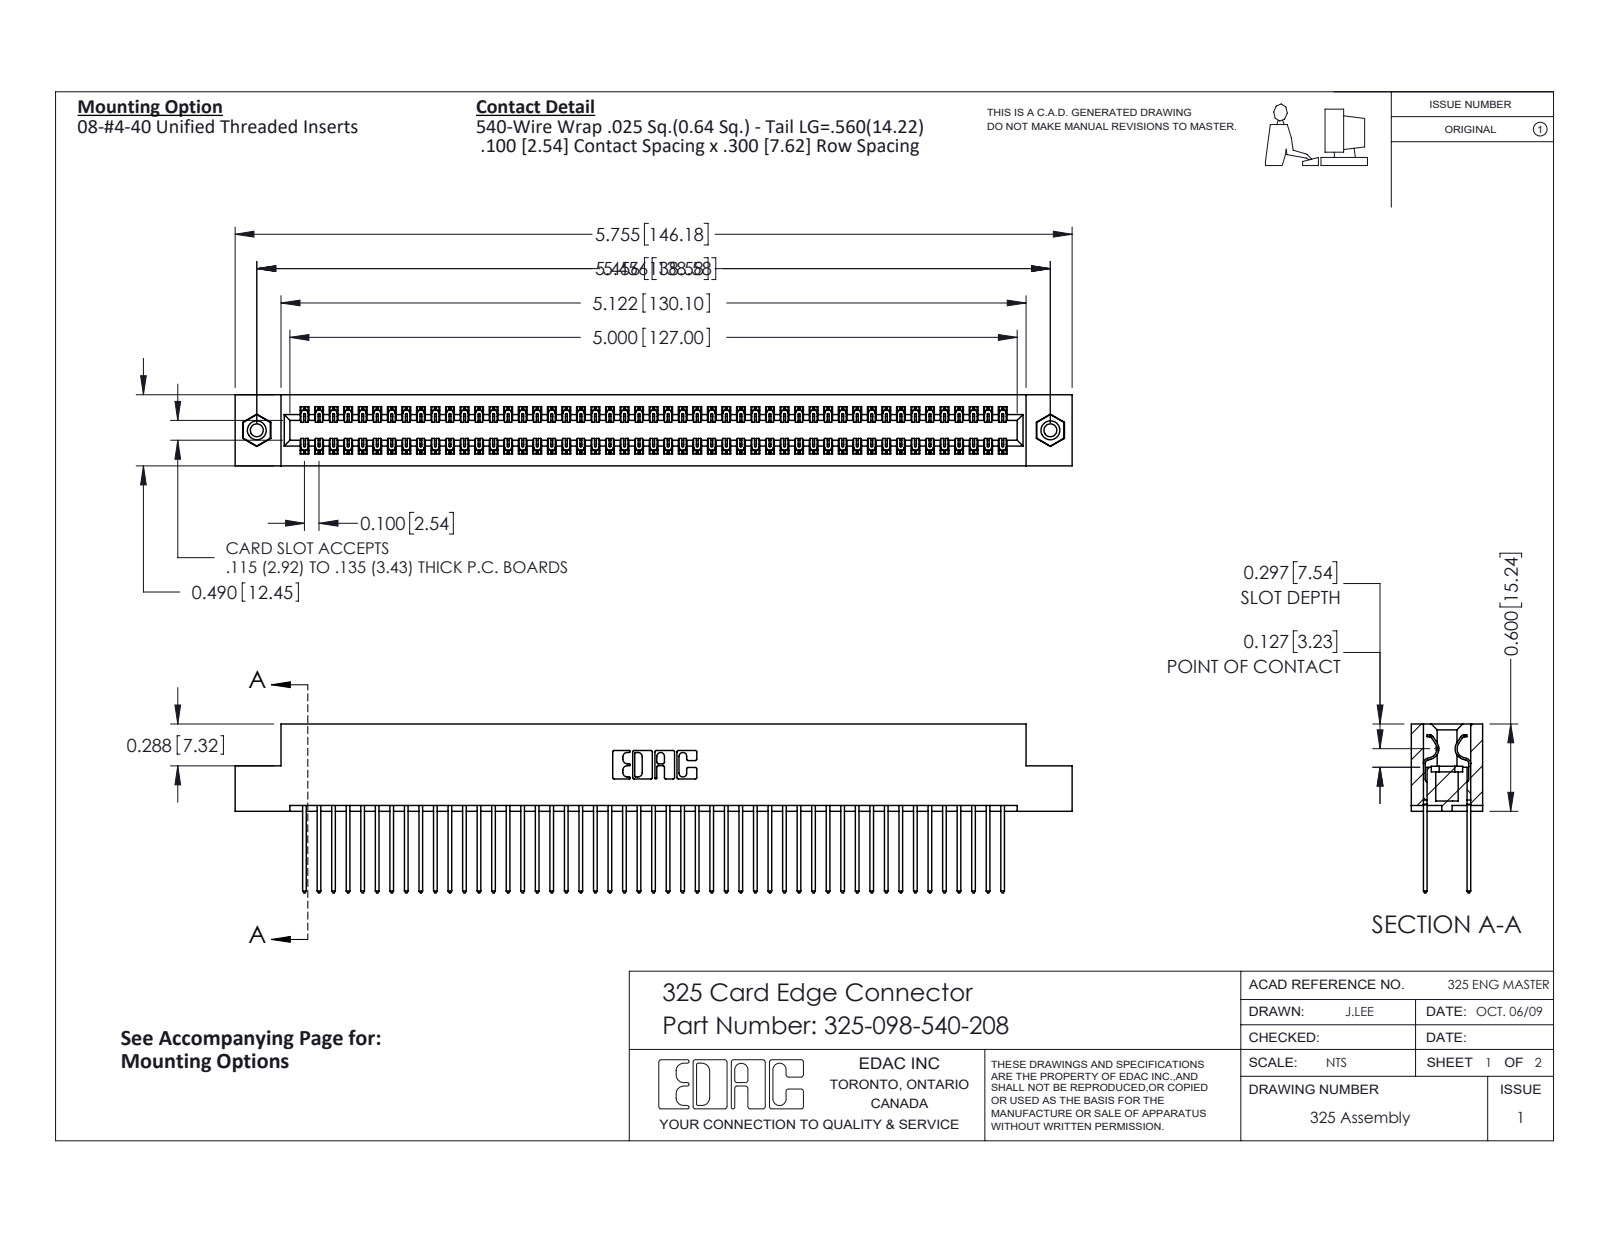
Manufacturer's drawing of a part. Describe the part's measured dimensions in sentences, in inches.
The part is named "325-292-001_325-293-140; 325-098-540-208; 345-250-001_345-250-003-102; 325 Part_TI". Its 3-D file was written by "SolidWorks 2016 (CONFIG_CONTROL_DESIGN)". It is 101 solids with 5270 faces: 3630 planar, 1624 cylindrical and 16 other. Overall it measures 5.755 by 1.16 by 0.49 inches. Its volume is 1.178 cubic inches and its surface area 39.23 square inches. Round holes: 2 of diameter 0.089, 2 of diameter 0.125, 2 of diameter 0.16. Round bosses or shafts: 2 of diameter 0.155. Partial cylindrical surfaces (rounded edges, fillets, slot ends): 147 of radius 0.006, 98 of radius 0.01, 22 of radius 0.01, 6 of radius 0.007, 6 of radius 0.031, 3 of radius 0.026, 2 of radius 0.014, 2 of radius 0.022. The main face-to-face distances are 0.083, 0.407, 0.3, 0.107, 0.383, 0.025, 0.325, 0.49, 0.275, 0.56. The hole center spacings are 5.456.
